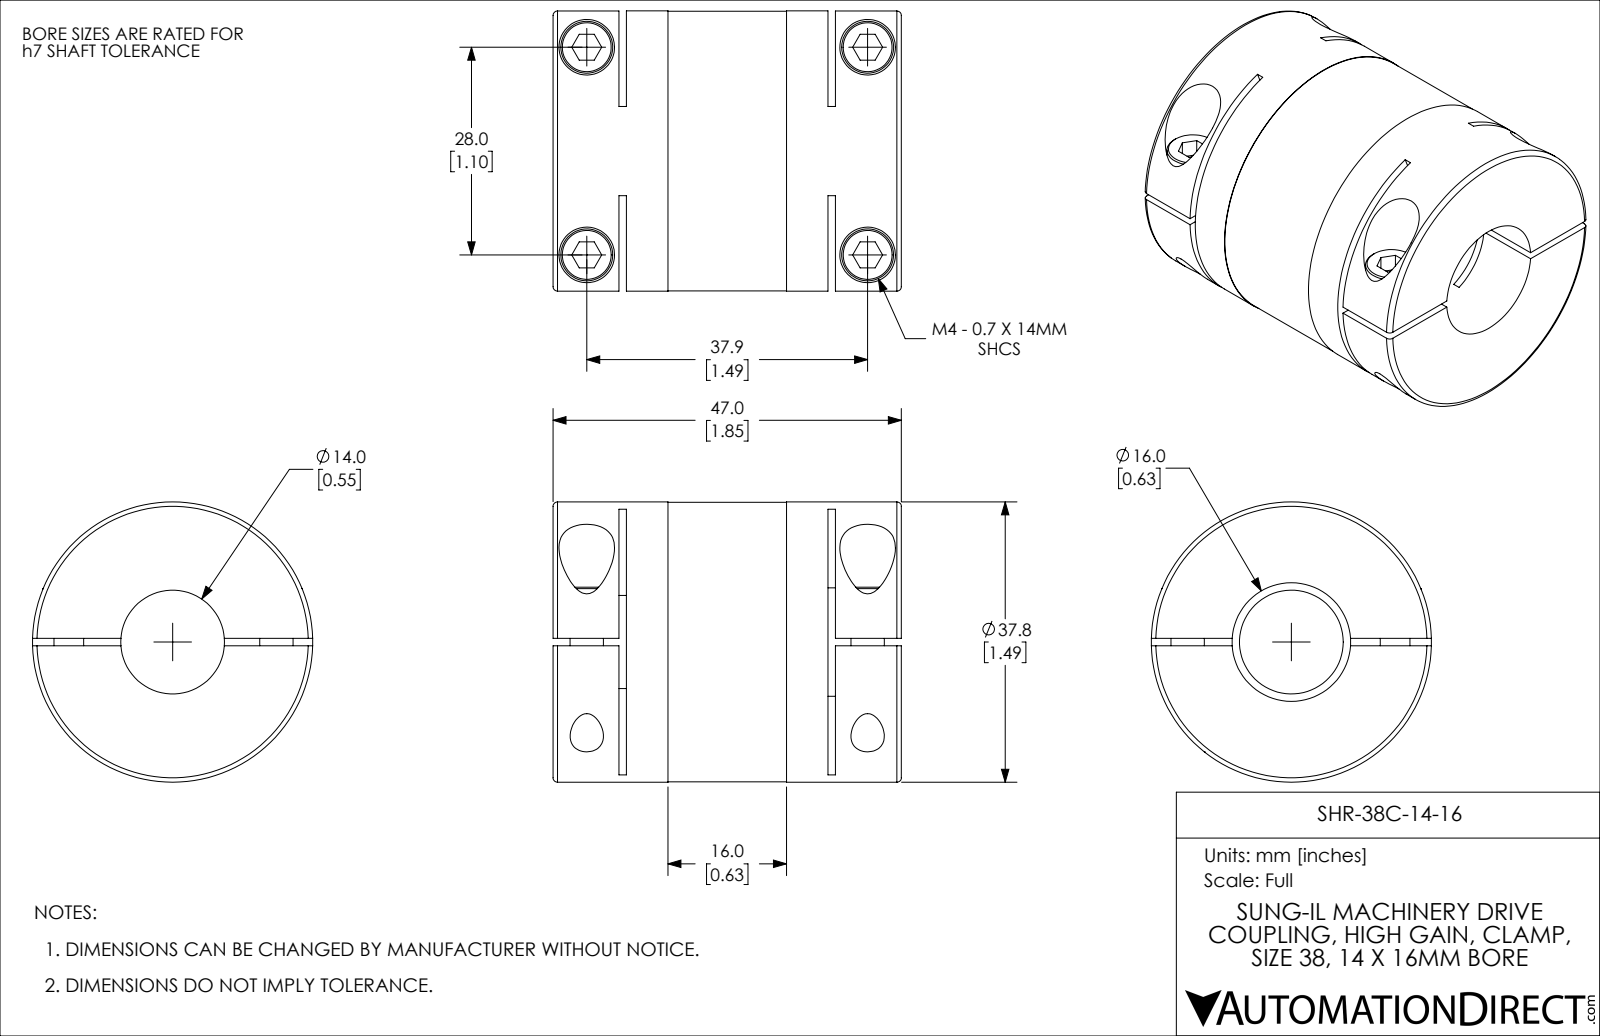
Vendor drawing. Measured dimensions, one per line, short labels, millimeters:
name: SHR-38C-14-16
written by: SolidWorks 2021 (CONFIG_CONTROL_DESIGN)
unit: mm
bodies: 1 solid, 144 faces (70 planar, 58 cylindrical, 16 other)
size: 47 × 37.8 × 37.8
volume: 39 883 mm³; area: 15 241 mm²
holes: 4× ⌀4.5, 4× ⌀7.5, 1× ⌀14, 1× ⌀16, 1× ⌀18
bosses: 4× ⌀7, 2× ⌀4, 1× ⌀37.8, 1× ⌀37.7
rounds: 2× R50
face distances: 1, 9.9, 37.1, 8.9, 38.1, 28.2, 47, 27.2, 29.2, 31.5
hole spacings: 28, 37.9, 47.12
